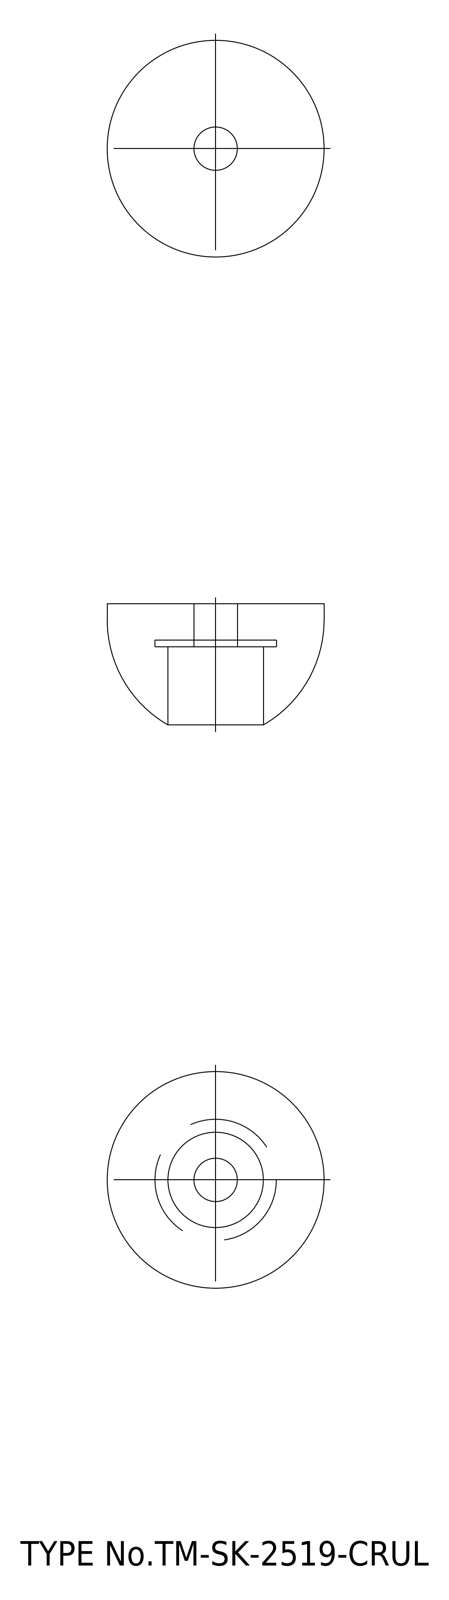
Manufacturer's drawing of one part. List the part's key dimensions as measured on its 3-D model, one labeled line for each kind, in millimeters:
Part name (STEP PRODUCT): rubber foot; washer
STEP written by: spGate 15.6.1 (AUTOMOTIVE_DESIGN)
Units: millimetres
Bodies: 2 solids, 19 faces (5 planar, 12 cylindrical, 2 other)
Overall size (bounding box): 25 × 25 × 14
Volume: 4 284 mm³ · Surface area: 2 468 mm²
Round holes (diameter × count): ⌀5 ×1, ⌀11 ×1, ⌀14 ×1
Round bosses / shafts (diameter × count): ⌀25 ×1
Main face-to-face distances: 4.2, 0.8, 5
